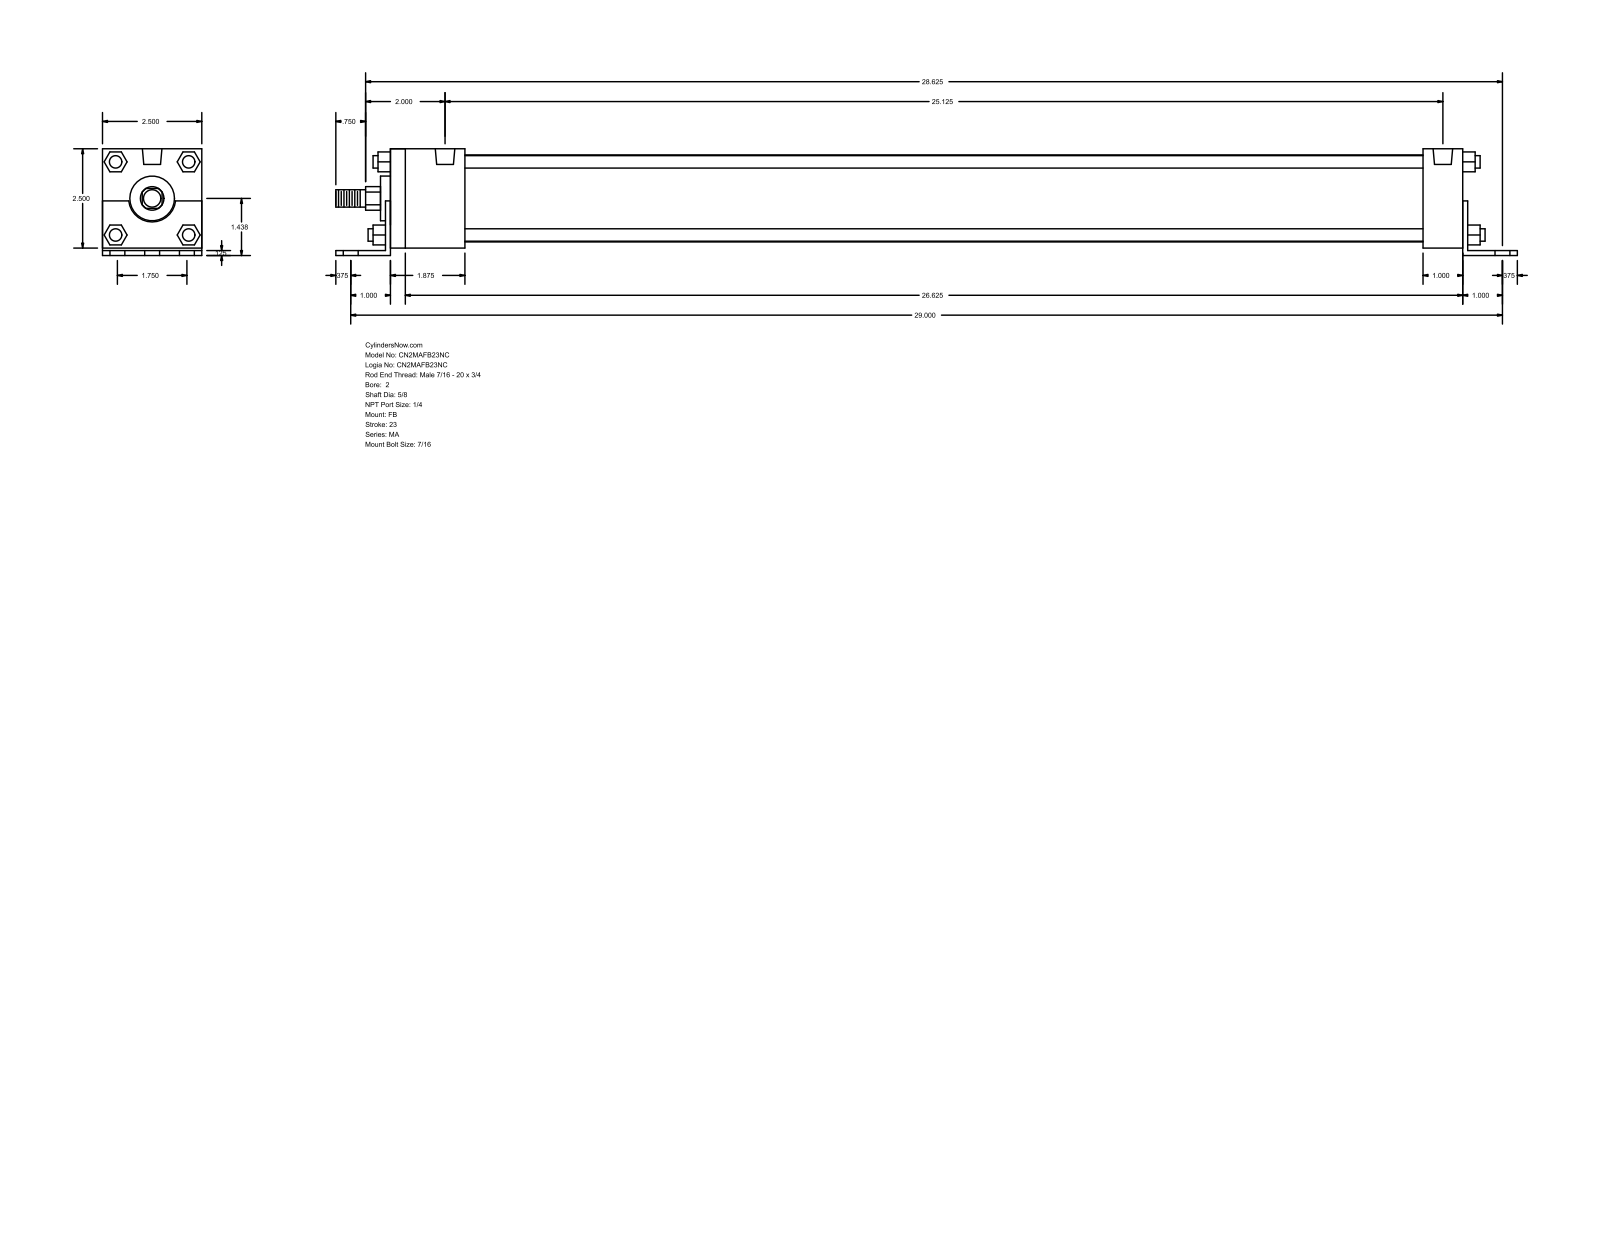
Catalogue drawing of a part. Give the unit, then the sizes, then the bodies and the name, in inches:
Units: inches
Overall size (bounding box): 29.75 × 2.687 × 2.5
Round holes (diameter × count): ⌀0.437 ×6, ⌀0.313 ×4, ⌀0.492 ×2
Round bosses / shafts (diameter × count): ⌀0.313 ×4, ⌀2.19 ×1, ⌀1.125 ×1, ⌀0.625 ×1, ⌀0.437 ×1
Partial cylindrical surfaces — rounded edges, fillets, slot ends (radius × count): R0.297 ×1, R0.593 ×1
Main face-to-face distances: 2.5, 0.187, 0.125, 2.687, 0.063, 0.125, 2.563, 27.125, 27, 1.125
Hole centre spacings: 0.875, 29.014, 29, 1.737, 1.75, 2.531, 25.125, 26.64
Bodies: 0 solids, 140 faces (105 planar, 35 cylindrical, 0 other)
Part name (STEP PRODUCT): MA_FB__0200_0.625
STEP written by: GSSL Pune (CONFIG_CONTROL_DESIGN)
